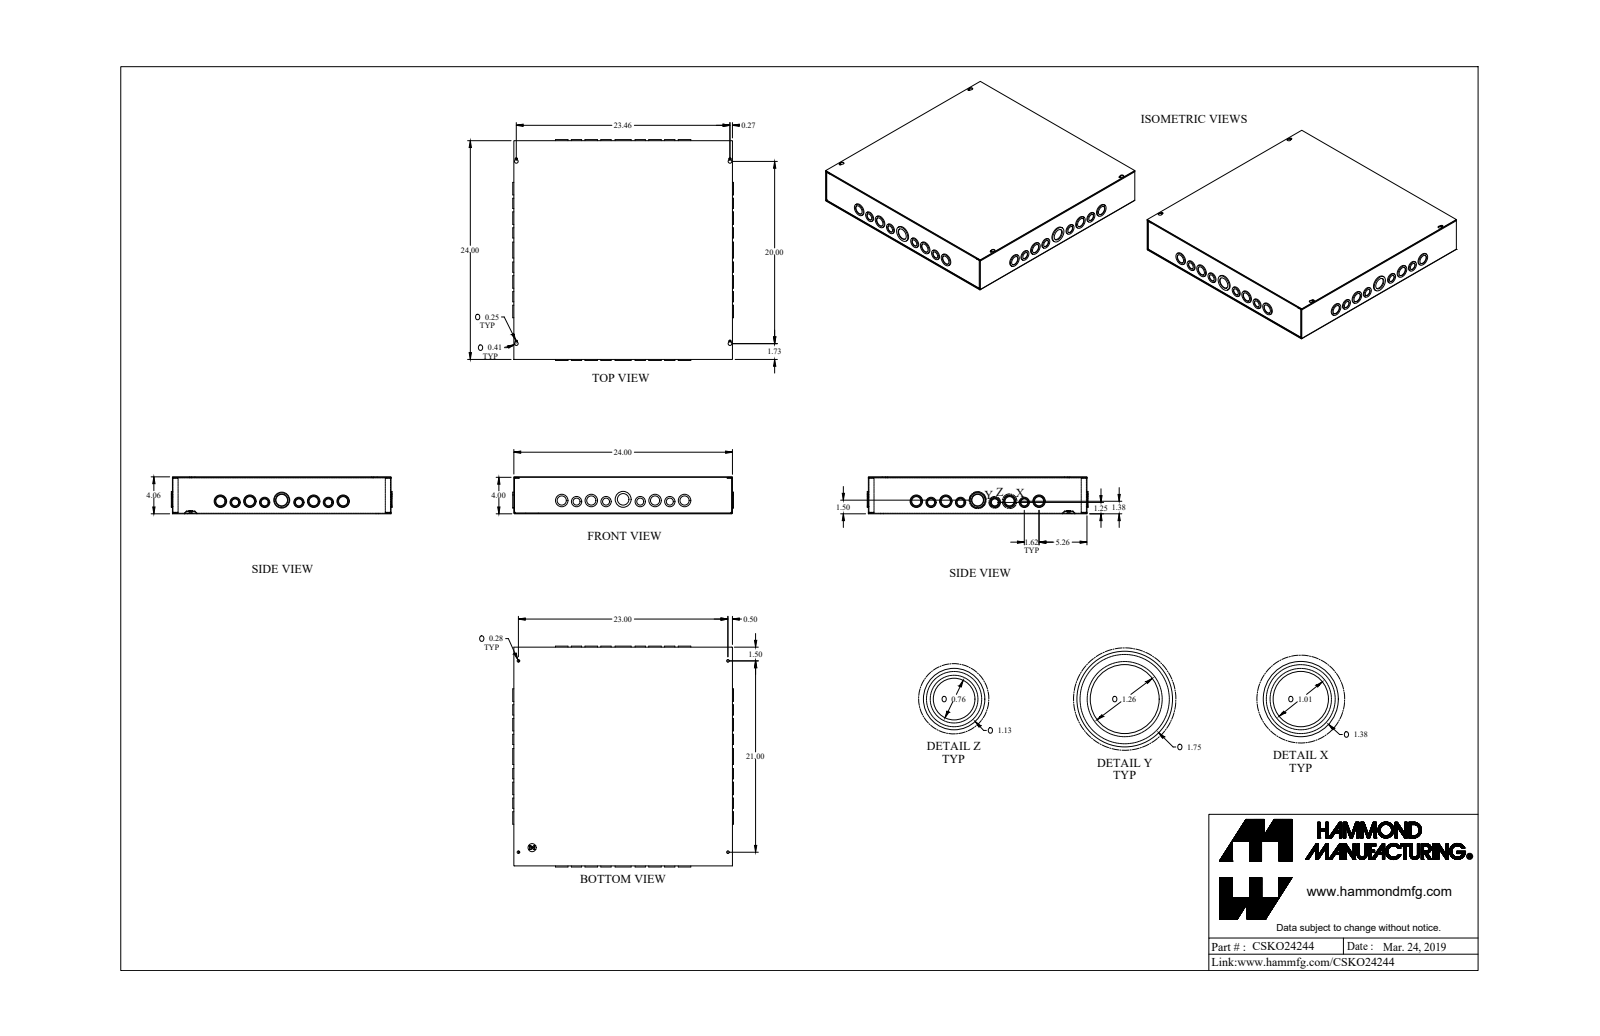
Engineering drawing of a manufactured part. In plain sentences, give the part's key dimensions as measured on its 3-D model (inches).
The part is named "CSKO24244_Default". Its 3-D file was written by "SolidWorks 2019 (CONFIG_CONTROL_DESIGN)". It is 4 solids with 637 faces: 269 planar, 360 cylindrical and 8 other. Overall it measures 24.234 by 24.234 by 4.057 inches. Its volume is 92.51 cubic inches and its surface area 3 266 square inches. Round holes: 16 of diameter 1.011, 10 of diameter 1.261, 8 of diameter 0.761, 5 of diameter 0.17, 4 of diameter 0.281, 2 of diameter 1.636, 1 of diameter 0.5. Round bosses or shafts: 14 of diameter 1.125, 9 of diameter 1.375, 8 of diameter 0.875, 4 of diameter 1.125, 4 of diameter 0.875, 2 of diameter 1.75, 1 of diameter 1.375, 1 of diameter 0.492. Partial cylindrical surfaces (rounded edges, fillets, slot ends): 12 of radius 0.029, 12 of radius 0.086, 8 of radius 0.057, 4 of radius 0.125, 4 of radius 0.203. The main face-to-face distances are 0.057, 4, 3.943, 4.057, 23.943, 24, 23.886, 0.114, 0.08, 3.863. The hole center spacings are 1.625, 3.24, 8.621, 7, 10.24, 0.55, 1.896, 3.502.
